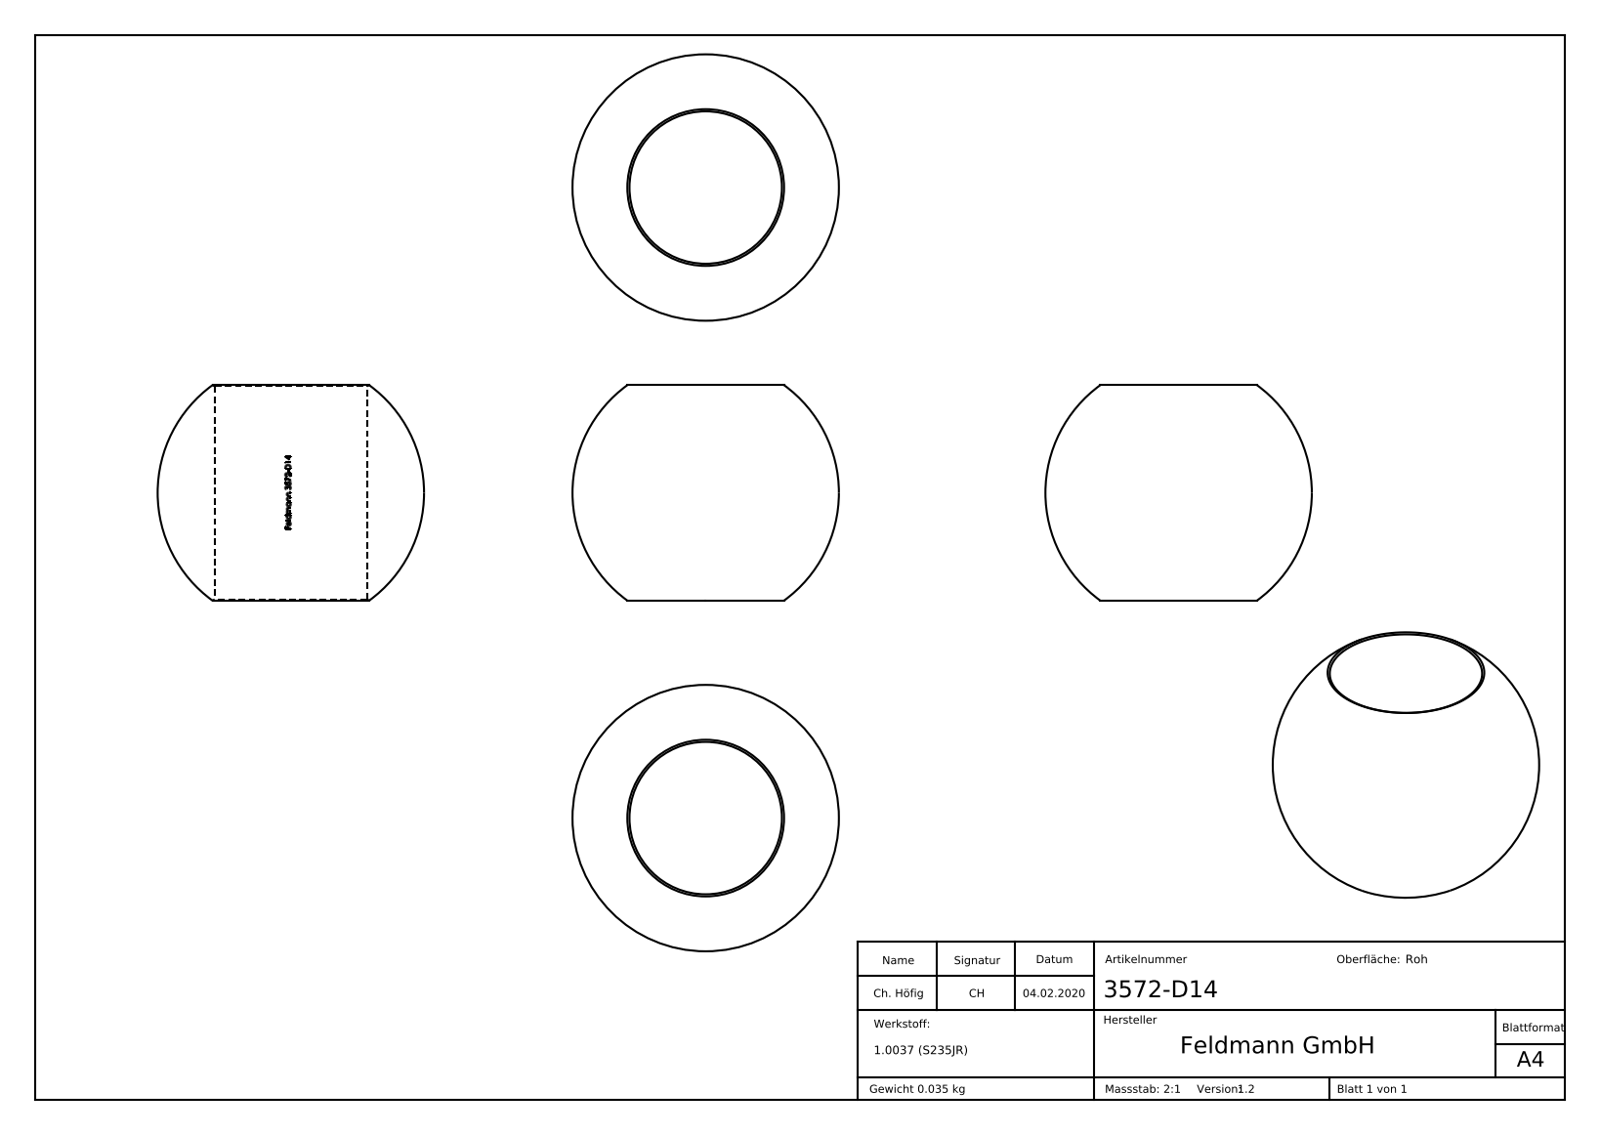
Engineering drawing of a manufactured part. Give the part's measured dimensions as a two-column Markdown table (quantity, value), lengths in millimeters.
| quantity | value |
| --- | --- |
| part name | 3572-D14 |
| STEP written by | SolidWorks 2015 (CONFIG_CONTROL_DESIGN) |
| units | millimeters |
| bodies | 1 solid, 212 faces (104 planar, 22 cylindrical, 86 other) |
| overall size | 25 × 25 × 20.22 |
| volume | 4 513 mm³ |
| surface area | 2 511 mm² |
| round holes (diameter × count) | 14.3 × 1 |
| partial cylindrical surfaces (radius × count) | 7.25 × 1 |
| main face-to-face distances | 4.83, 0.5, 5.48, 0.45, 0.53, 3.69, 0.35, 0.61, 2.54, 3.1 |
